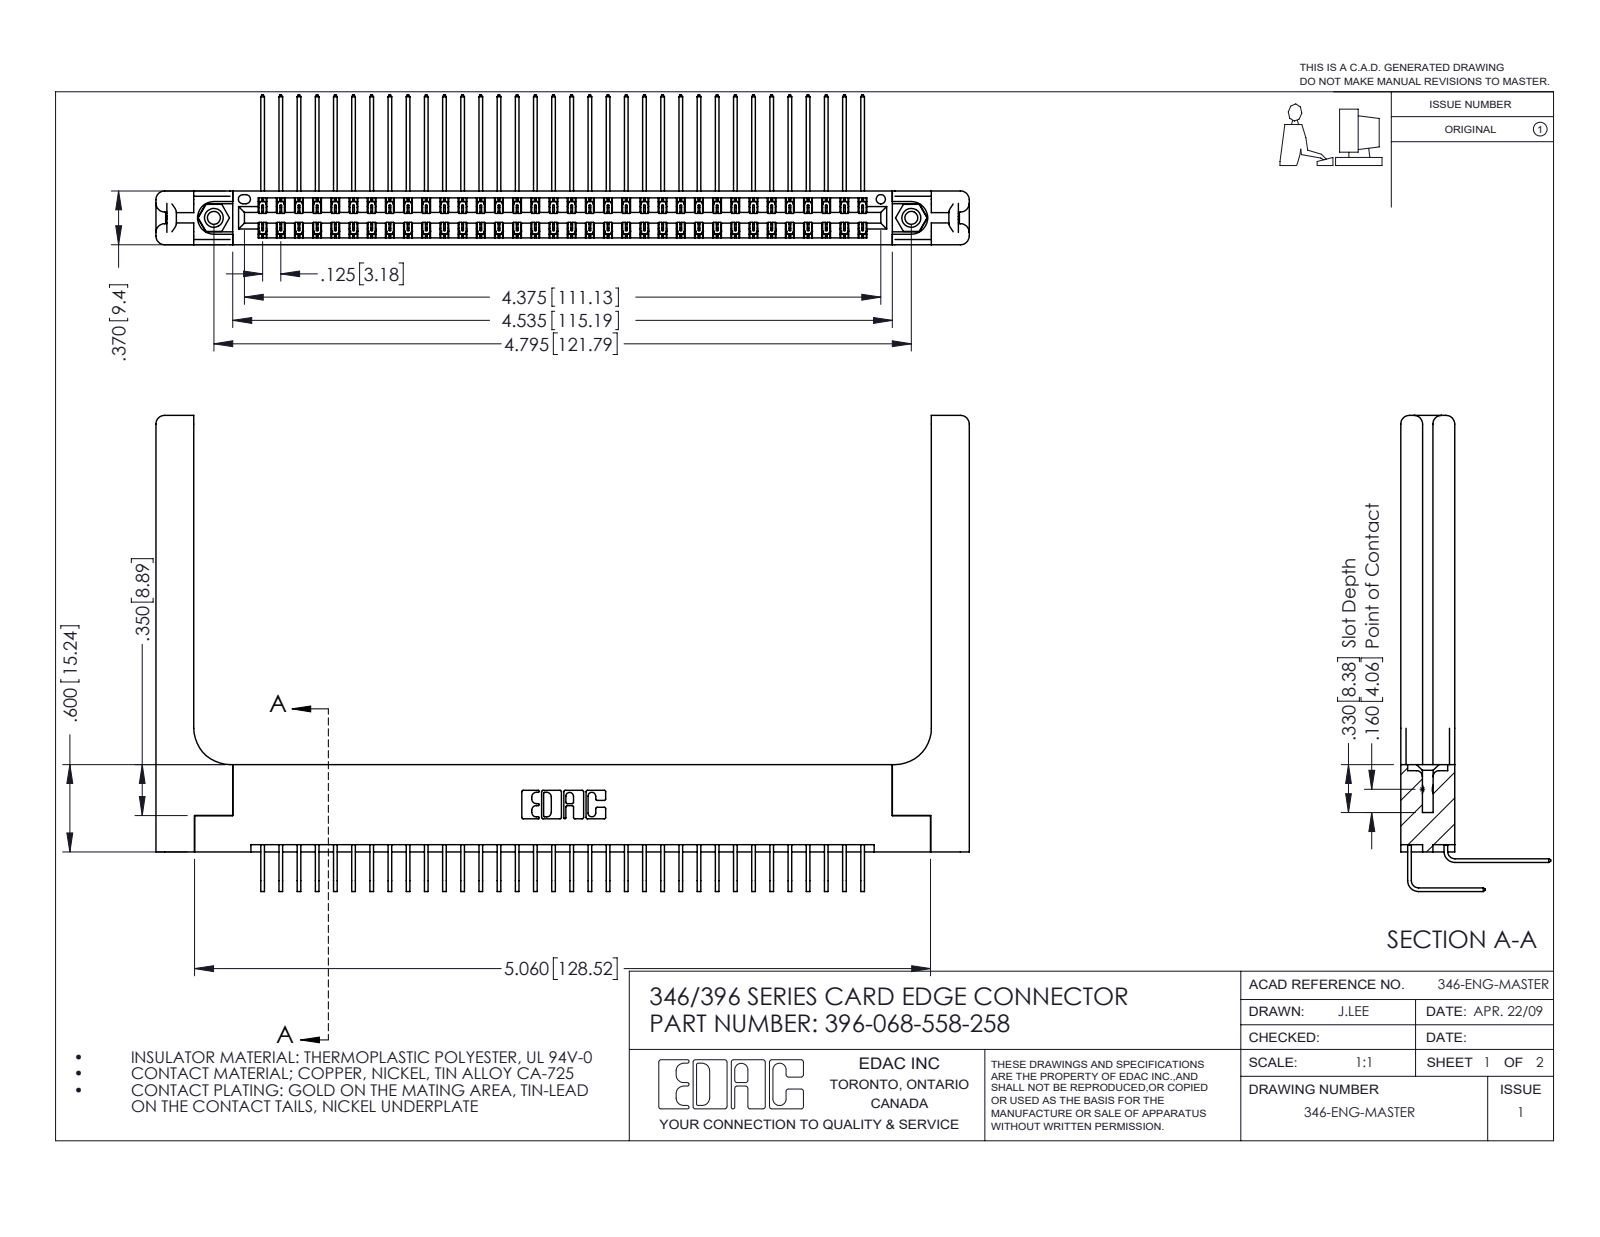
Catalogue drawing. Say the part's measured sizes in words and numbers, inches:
The part is named "345-250-001_345-250-001-102; 346-220-058_345-220-058; 396-068-558-258; 345-292-001_558 559 Tail - 1 (+2 more)". Its 3-D file was written by "SolidWorks 2016 (CONFIG_CONTROL_DESIGN)". It is 73 solids with 4050 faces: 2740 planar, 1250 cylindrical and 60 other. Overall it measures 5.591 by 3.273 by 1.03 inches. Its volume is 1.323 cubic inches and its surface area 40.64 square inches. Round holes: 2 of diameter 0.089, 2 of diameter 0.125, 2 of diameter 0.156, 1 of diameter 0.064. Round bosses or shafts: 2 of diameter 0.155. Partial cylindrical surfaces (rounded edges, fillets, slot ends): 102 of radius 0.006, 22 of radius 0.01, 16 of radius 0.06, 6 of radius 0.007, 6 of radius 0.031, 3 of radius 0.026, 2 of radius 0.014, 2 of radius 0.022. The main face-to-face distances are 0.322, 0.048, 0.37, 0.072, 0.025, 0.298, 0.148, 0.15, 0.25, 0.275. The hole center spacings are 0.246, 4.587, 4.795.
